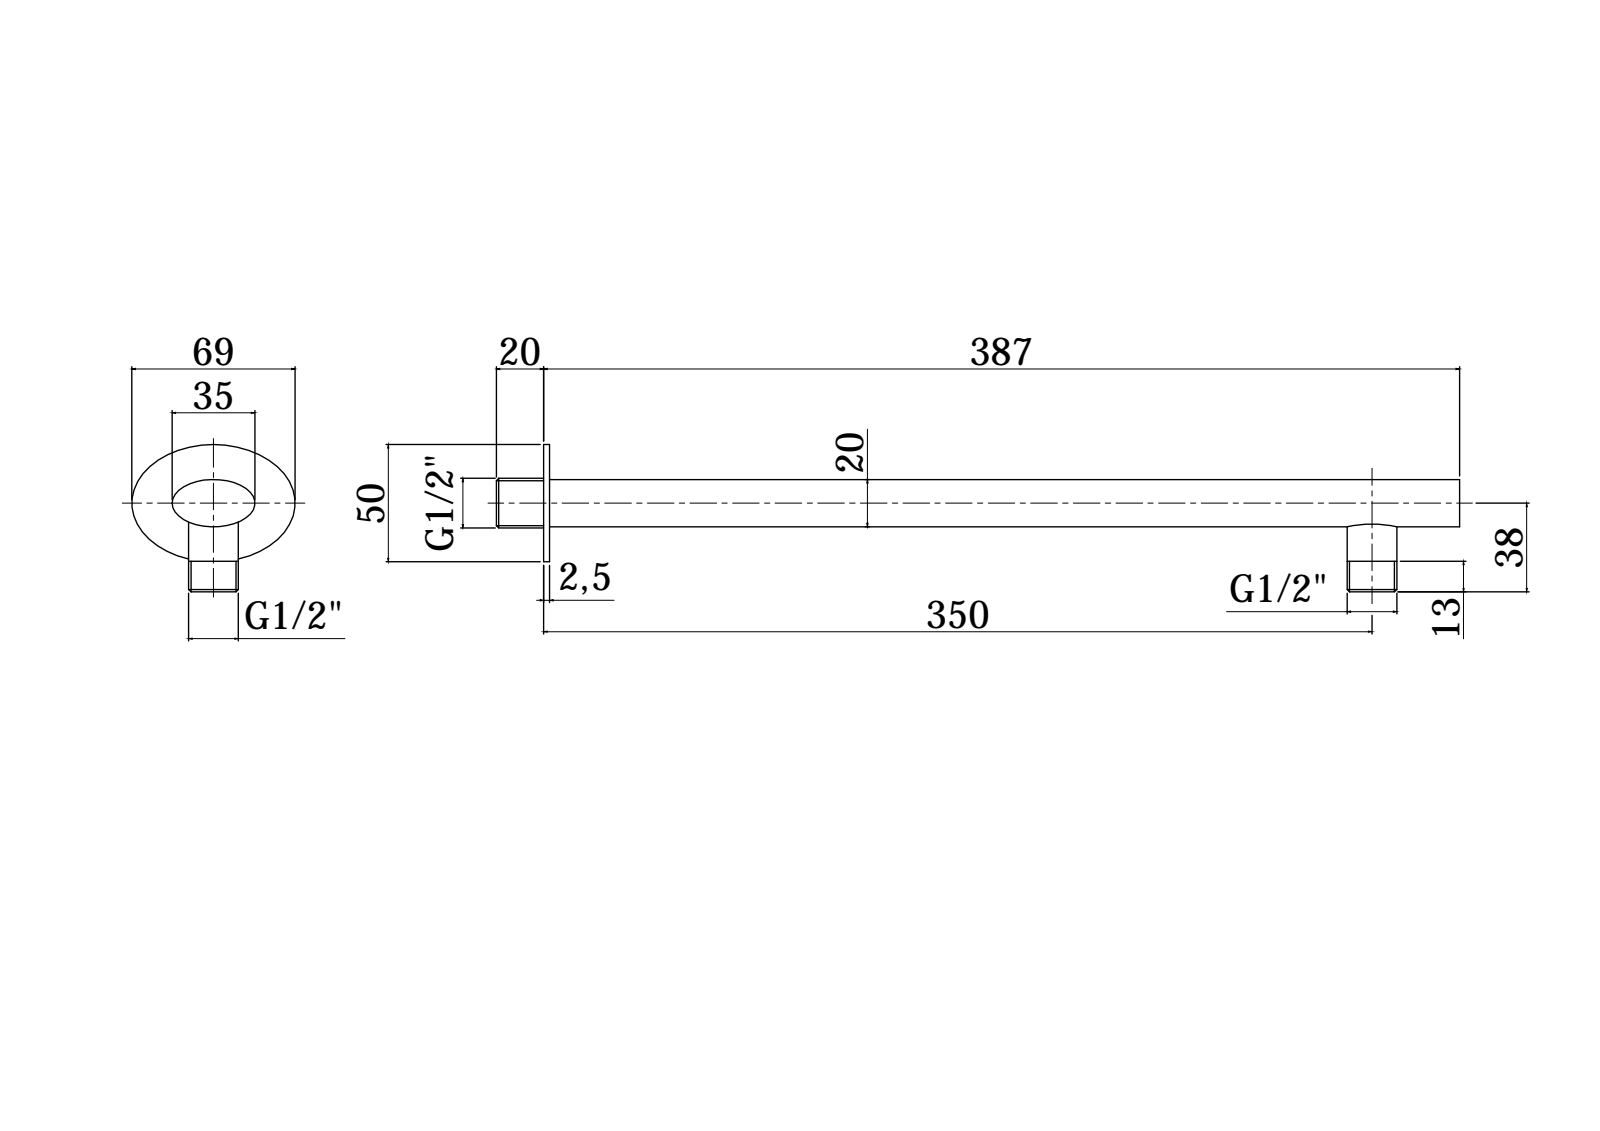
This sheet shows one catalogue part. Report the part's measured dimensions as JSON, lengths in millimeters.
{"part_name": "ZSOF090CR", "step_written_by": "CREO PARAMETRIC BY PTC INC, 2020044 (CONFIG_CONTROL_DESIGN)", "units": "millimeters", "bodies": {"solids": 1, "faces": 102, "planar": 60, "cylindrical": 22, "other": 20}, "overall_size": [384.5, 70, 62], "volume_mm3": 52473, "surface_area_mm2": 74558, "round_holes": [[18, 2], [10, 1], [10.5, 1], [14, 1], [15, 1], [16, 1]], "round_bosses_or_shafts": [[21, 1], [15.5, 1], [14, 1]], "face_to_face_distances": [2.5, 384.5, 382, 1.2, 383.3, 380.8, 8, 10.5, 372.8, 374]}
